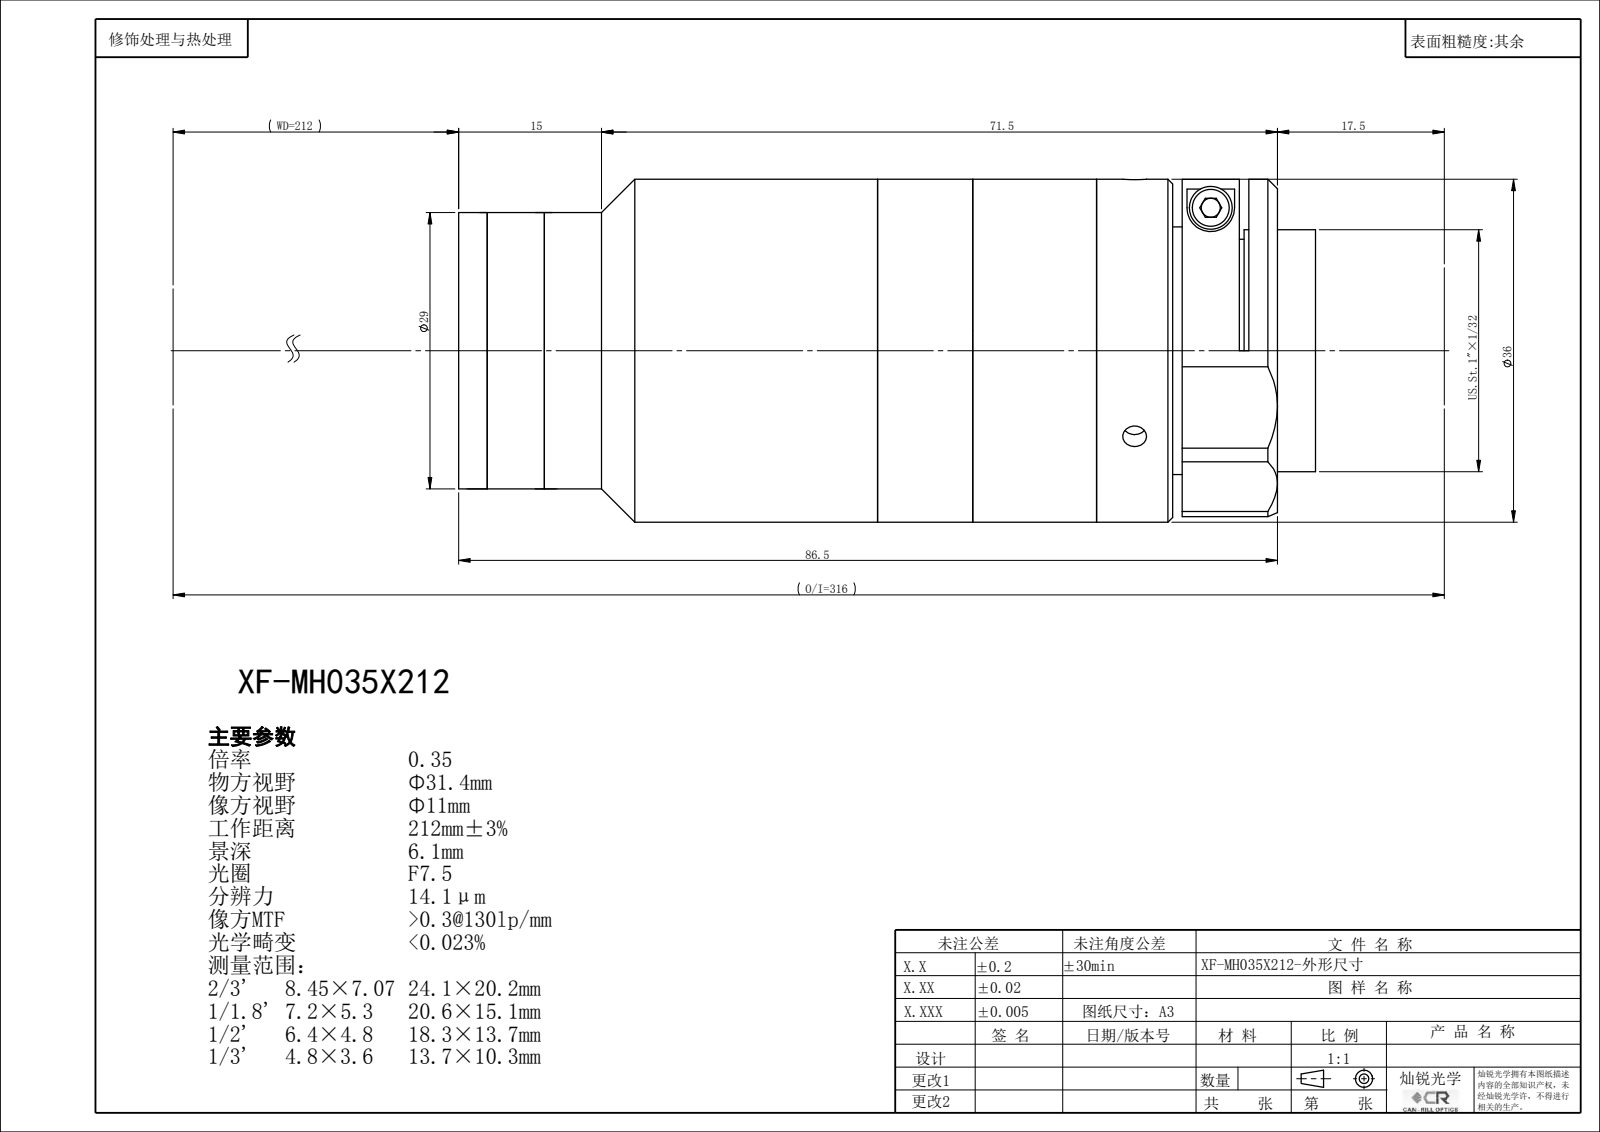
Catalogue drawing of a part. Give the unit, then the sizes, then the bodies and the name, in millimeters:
Units: millimetres
Overall size (bounding box): 90.49 × 36 × 36
Round holes (diameter × count): ⌀2.5 ×3, ⌀18 ×1, ⌀22.4 ×1, ⌀24 ×1, ⌀24.9 ×1, ⌀26.4 ×1
Round bosses / shafts (diameter × count): ⌀36 ×1, ⌀34 ×1, ⌀29 ×1, ⌀25.4 ×1
Main face-to-face distances: 1.5, 30.99, 32.49, 10, 40.99, 42.49, 81.49, 40.5, 50.5, 82.99
Bodies: 0 solids, 123 faces (59 planar, 42 cylindrical, 22 other)
Part name (STEP PRODUCT): XF-MH035X212
STEP written by: SolidWorks 2022 (CONFIG_CONTROL_DESIGN)
